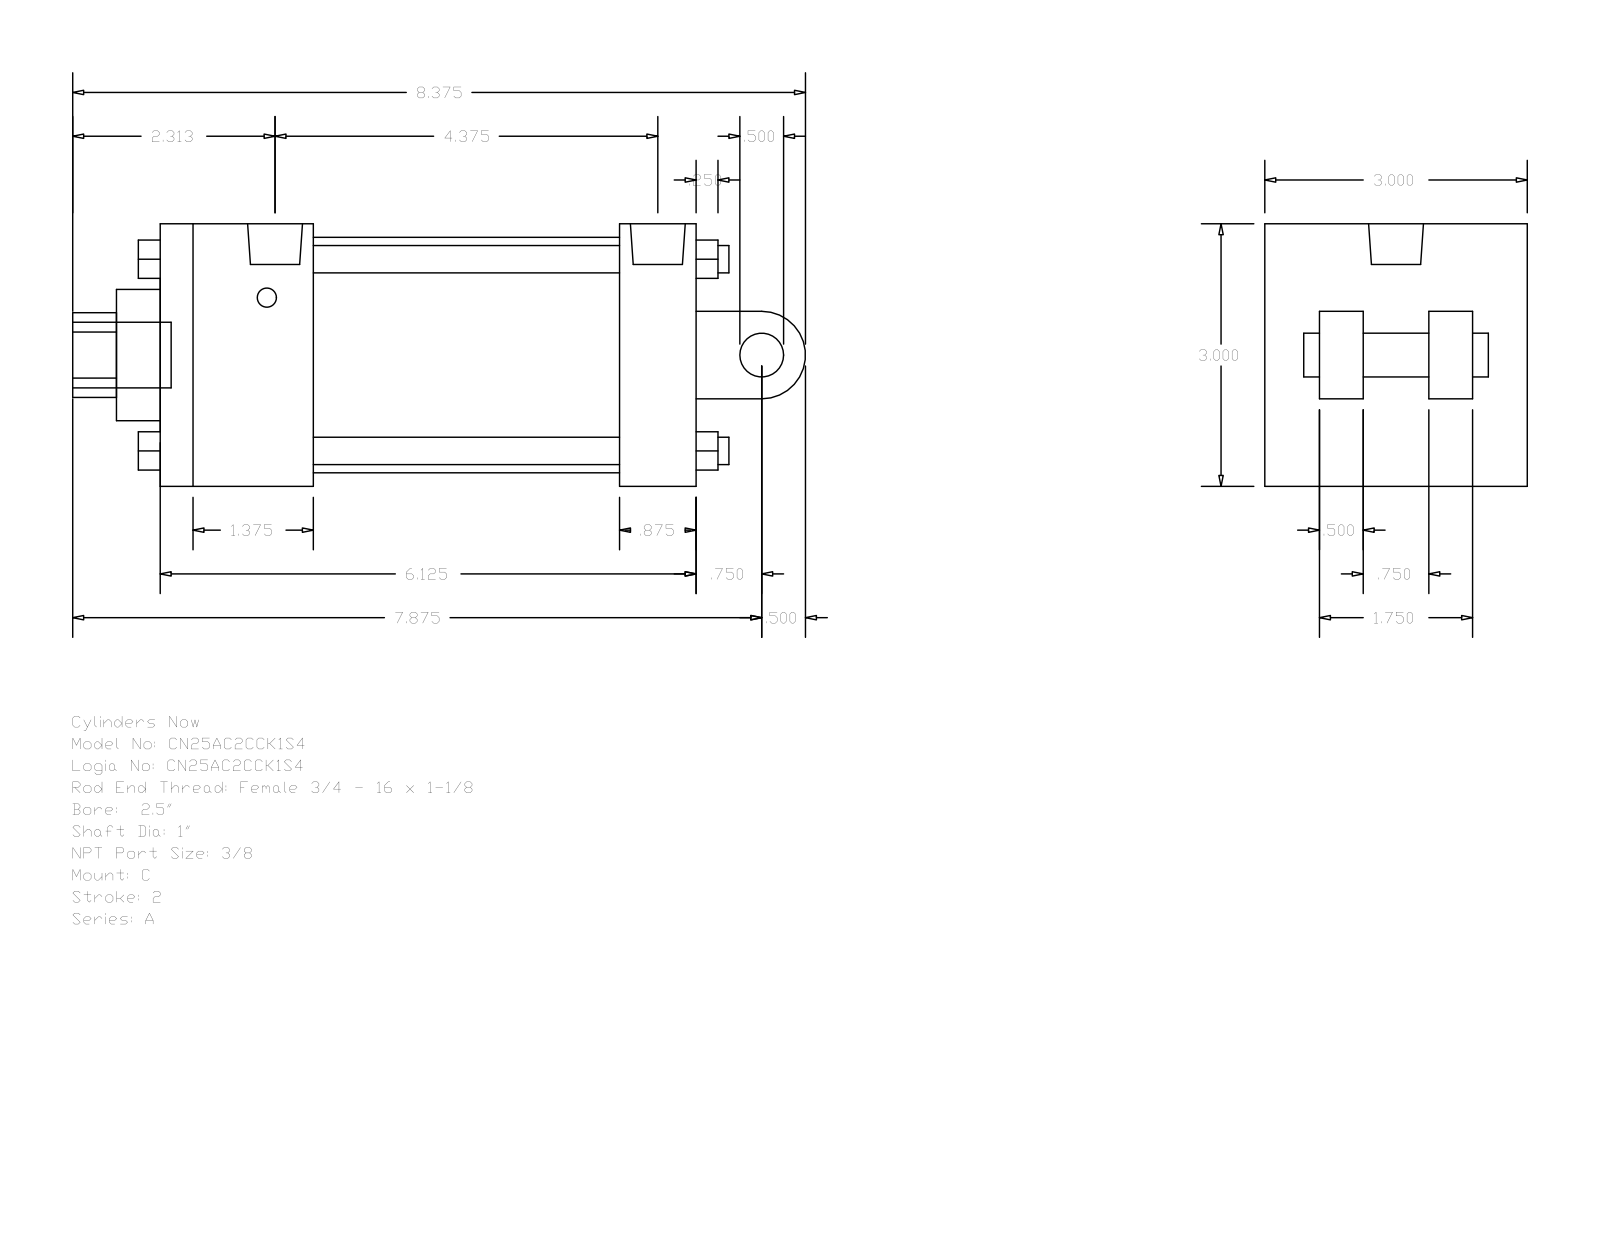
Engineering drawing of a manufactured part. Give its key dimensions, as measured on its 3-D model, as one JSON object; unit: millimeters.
{"part_name": "A_C__0250_1", "step_written_by": "GSSL Pune (CONFIG_CONTROL_DESIGN)", "units": "millimeters", "bodies": {"solids": 0, "faces": 135, "planar": 102, "cylindrical": 33, "other": 0}, "overall_size": [212.72, 76.2, 76.2], "round_holes": [[5.56, 2], [15.93, 1], [25.4, 1], [38.1, 1], [68.33, 1]], "round_bosses_or_shafts": [[7.94, 4], [5.56, 2], [19.05, 1], [15.93, 1], [12.7, 1]], "partial_cylinders_radius": [[12.29, 1], [12.7, 1]], "face_to_face_distances": [76.2, 155.57, 12.7, 44.45, 133.35, 88.9, 111.12, 22.22, 15.87, 25.4], "hole_center_spacings": [2.38]}
